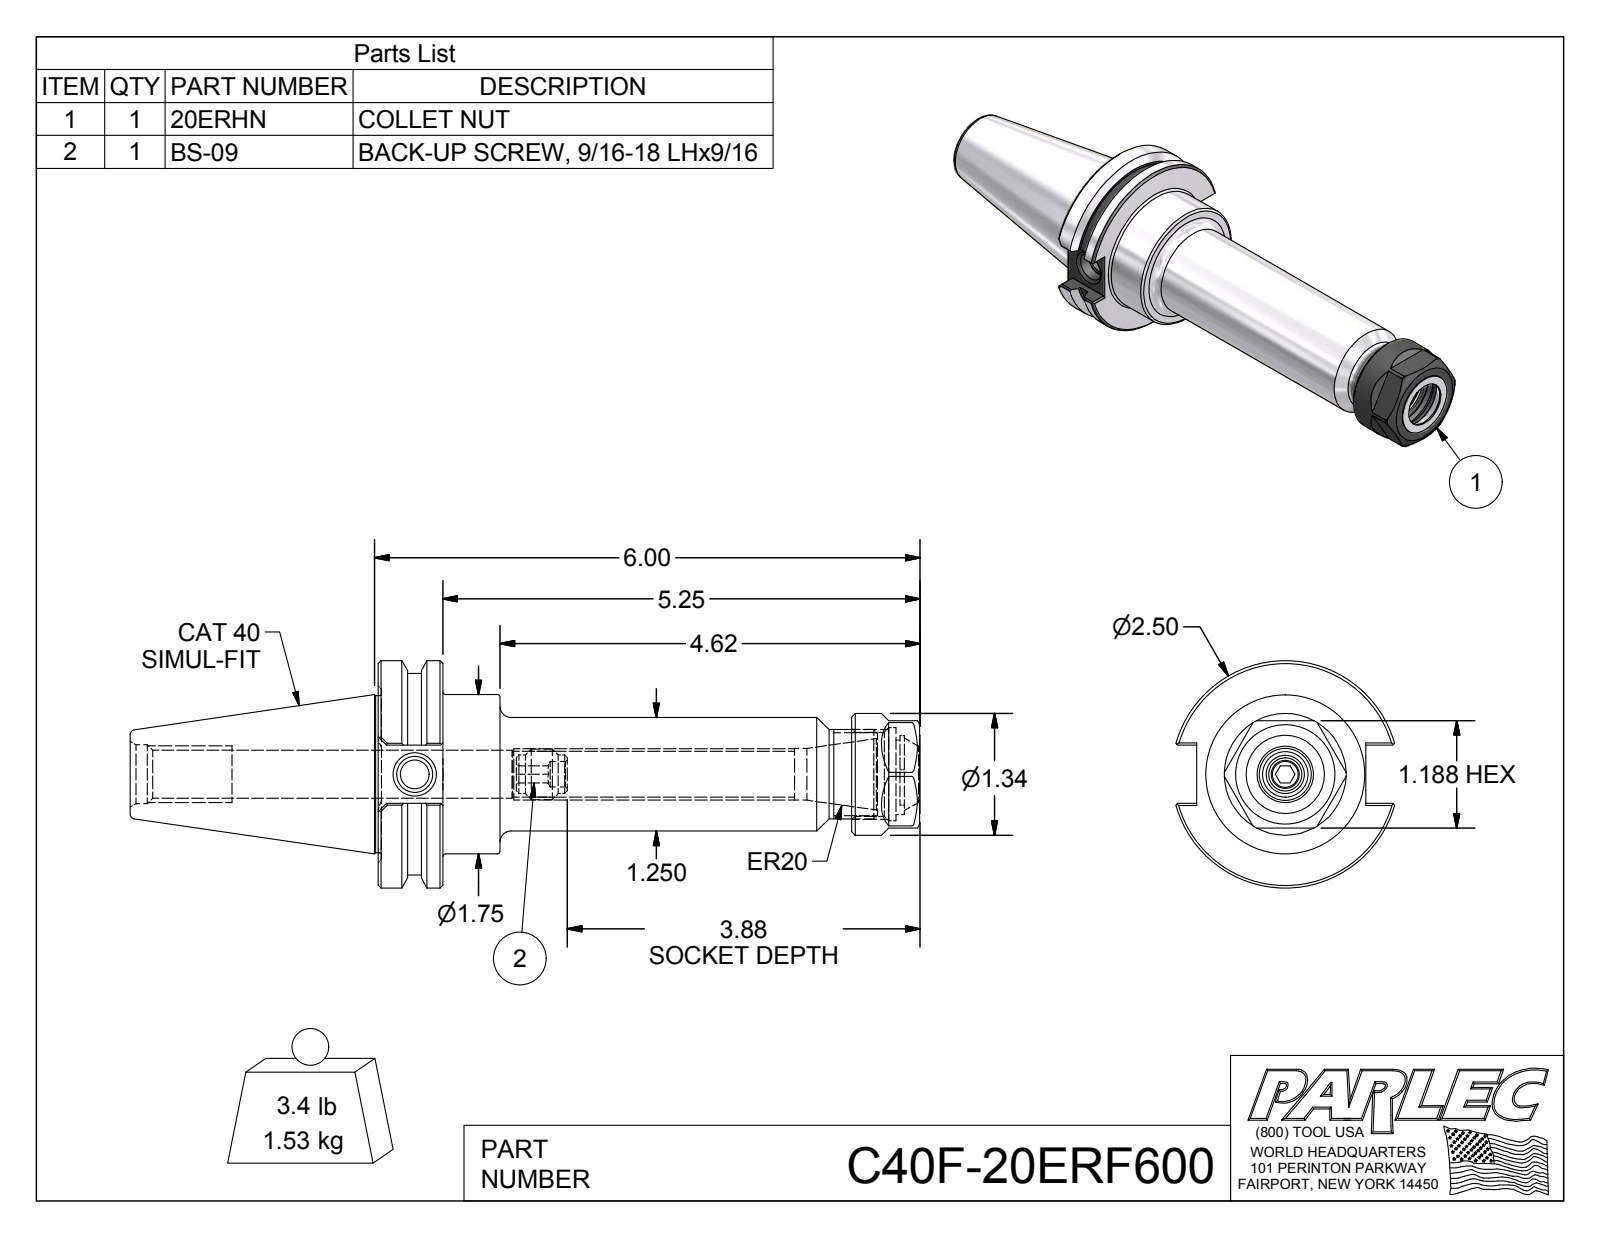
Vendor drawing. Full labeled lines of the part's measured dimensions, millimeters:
Part name (STEP PRODUCT): C40F-20ER6-1; 20ERHN; BS-09; C40F-20ERF600
STEP written by: Autodesk Inventor 2016 (AUTOMOTIVE_DESIGN)
Units: millimetres
Bodies: 3 solids, 136 faces (64 planar, 26 cylindrical, 46 other)
Overall size (bounding box): 220.66 × 63.5 × 61.11
Volume: 198 713 mm³ · Surface area: 43 105 mm²
Round holes (diameter × count): ⌀7.14 ×1, ⌀8 ×1, ⌀10.13 ×1, ⌀12.75 ×1, ⌀13.39 ×1, ⌀14.48 ×1, ⌀15.49 ×1, ⌀16.46 ×1, ⌀23.5 ×1, ⌀26 ×1
Round bosses / shafts (diameter × count): ⌀63.5 ×1, ⌀56.26 ×1, ⌀44.45 ×1, ⌀34 ×1, ⌀31.75 ×1, ⌀25 ×1, ⌀14.1 ×1, ⌀10.72 ×1
Partial cylindrical surfaces — rounded edges, fillets, slot ends (radius × count): R9.47 ×1, R10.55 ×1, R10.75 ×1
Main face-to-face distances: 18.04, 151.39, 133.35, 30, 34.04, 16, 117.35, 132.32, 114.28, 98.28
